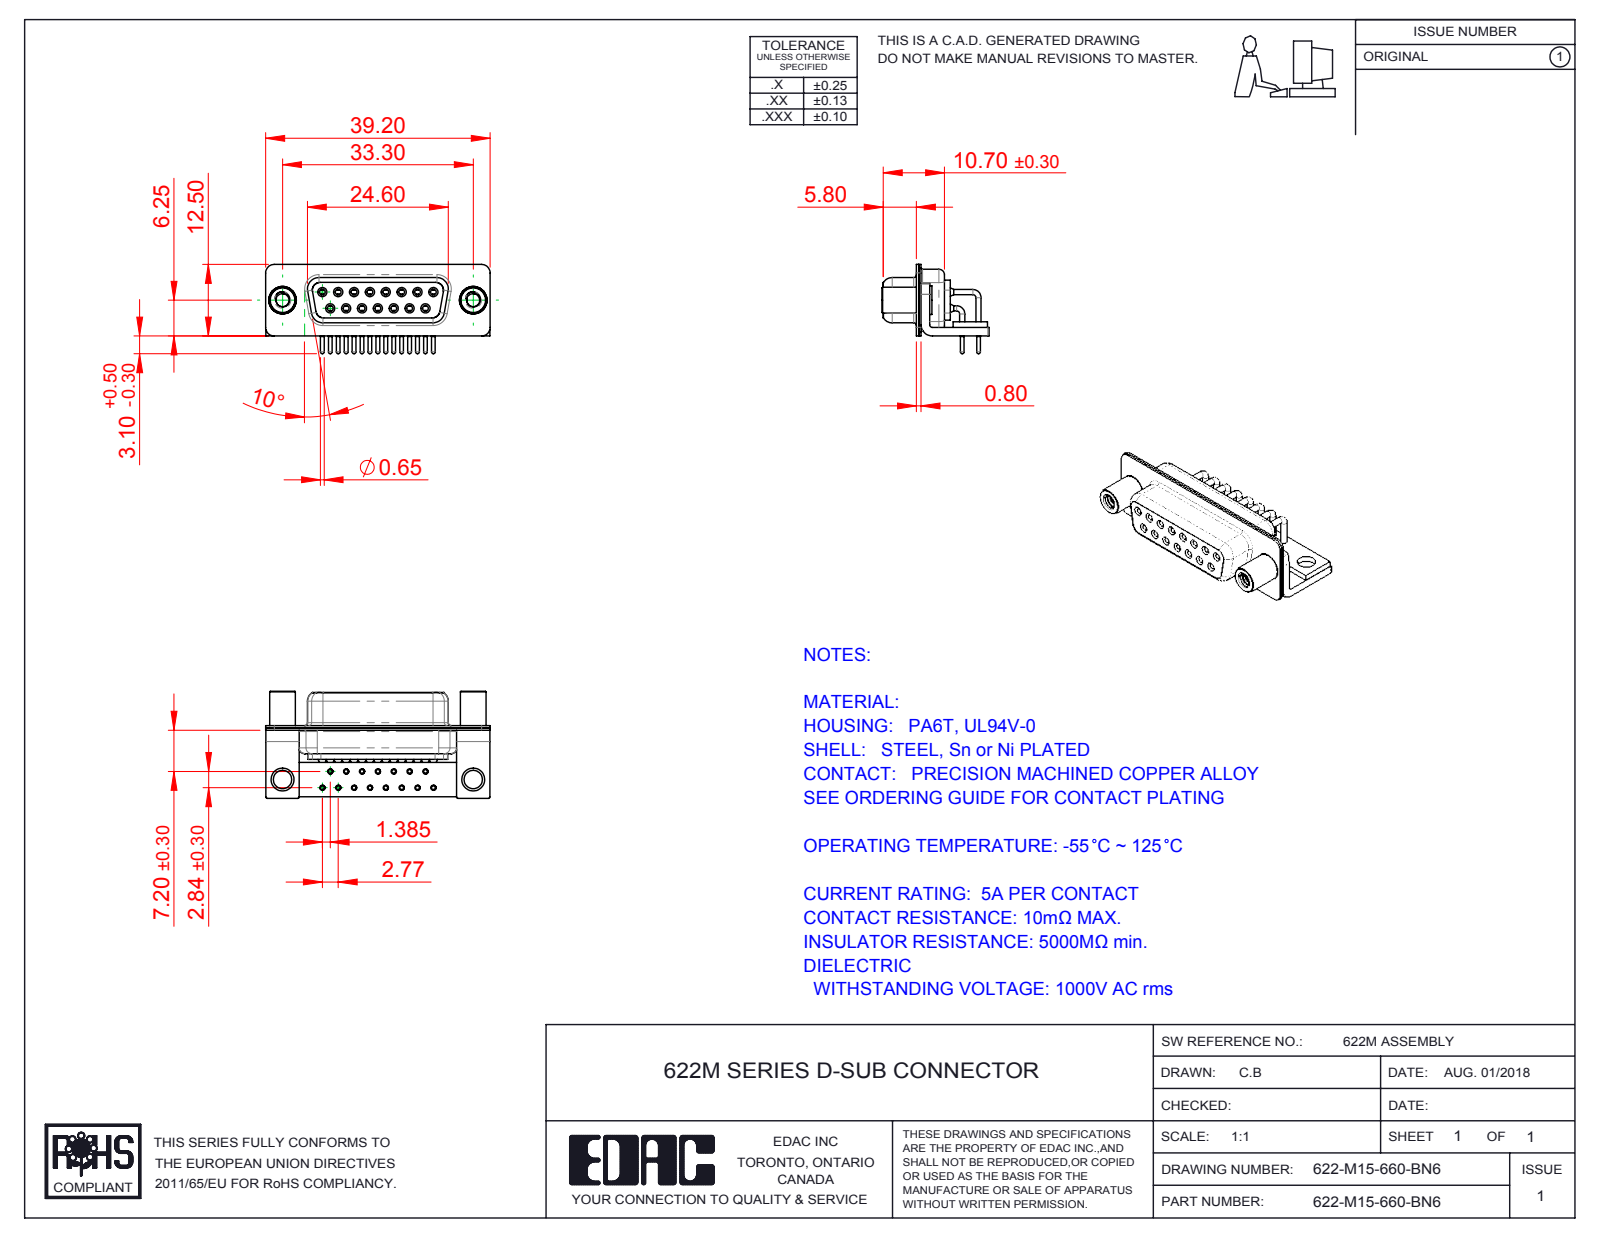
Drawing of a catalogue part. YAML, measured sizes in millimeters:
part_name: "622M Shell Rear_15 Contacts; 622M Shell Front_15 Contacts; 622M Housing_15 Contacts; 622-M15-660-BN6 (+5 more)"
step_written_by: "SolidWorks 2016 (CONFIG_CONTROL_DESIGN)"
units: millimeters
bodies: {solids: 23, faces: 1204, planar: 320, cylindrical: 576, other: 308}
overall_size: [39.2, 18.7, 15.6]
volume: 3100
surface_area: 7827
round_holes:
  - {diameter: 0.9, count: 15}
  - {diameter: 1, count: 15}
  - {diameter: 1.1, count: 15}
  - {diameter: 1.7, count: 15}
  - {diameter: 1.8, count: 15}
  - {diameter: 2, count: 15}
  - {diameter: 2.26, count: 2}
  - {diameter: 3.2, count: 2}
  - {diameter: 4, count: 2}
  - {diameter: 4.8, count: 2}
round_bosses_or_shafts:
  - {diameter: 0.9, count: 22}
  - {diameter: 1.6, count: 15}
  - {diameter: 1.5, count: 15}
  - {diameter: 0.65, count: 15}
  - {diameter: 5, count: 2}
  - {diameter: 4.9, count: 2}
  - {diameter: 4.5, count: 2}
partial_cylinders:
  - {radius: 0.25, count: 16}
  - {radius: 1.5, count: 16}
  - {radius: 2, count: 13}
  - {radius: 1.35, count: 8}
  - {radius: 1.6, count: 8}
  - {radius: 0.5, count: 5}
  - {radius: 0.6, count: 4}
  - {radius: 0.65, count: 4}
face_to_face_distances: [0.4, 2.3, 1.9, 0.8, 9.35, 1.5, 1, 1.45, 8.95, 0.85]
hole_center_spacings: [3.16, 2.77, 5.54, 8.31, 11.08, 5.03, 5.04, 7.48]
